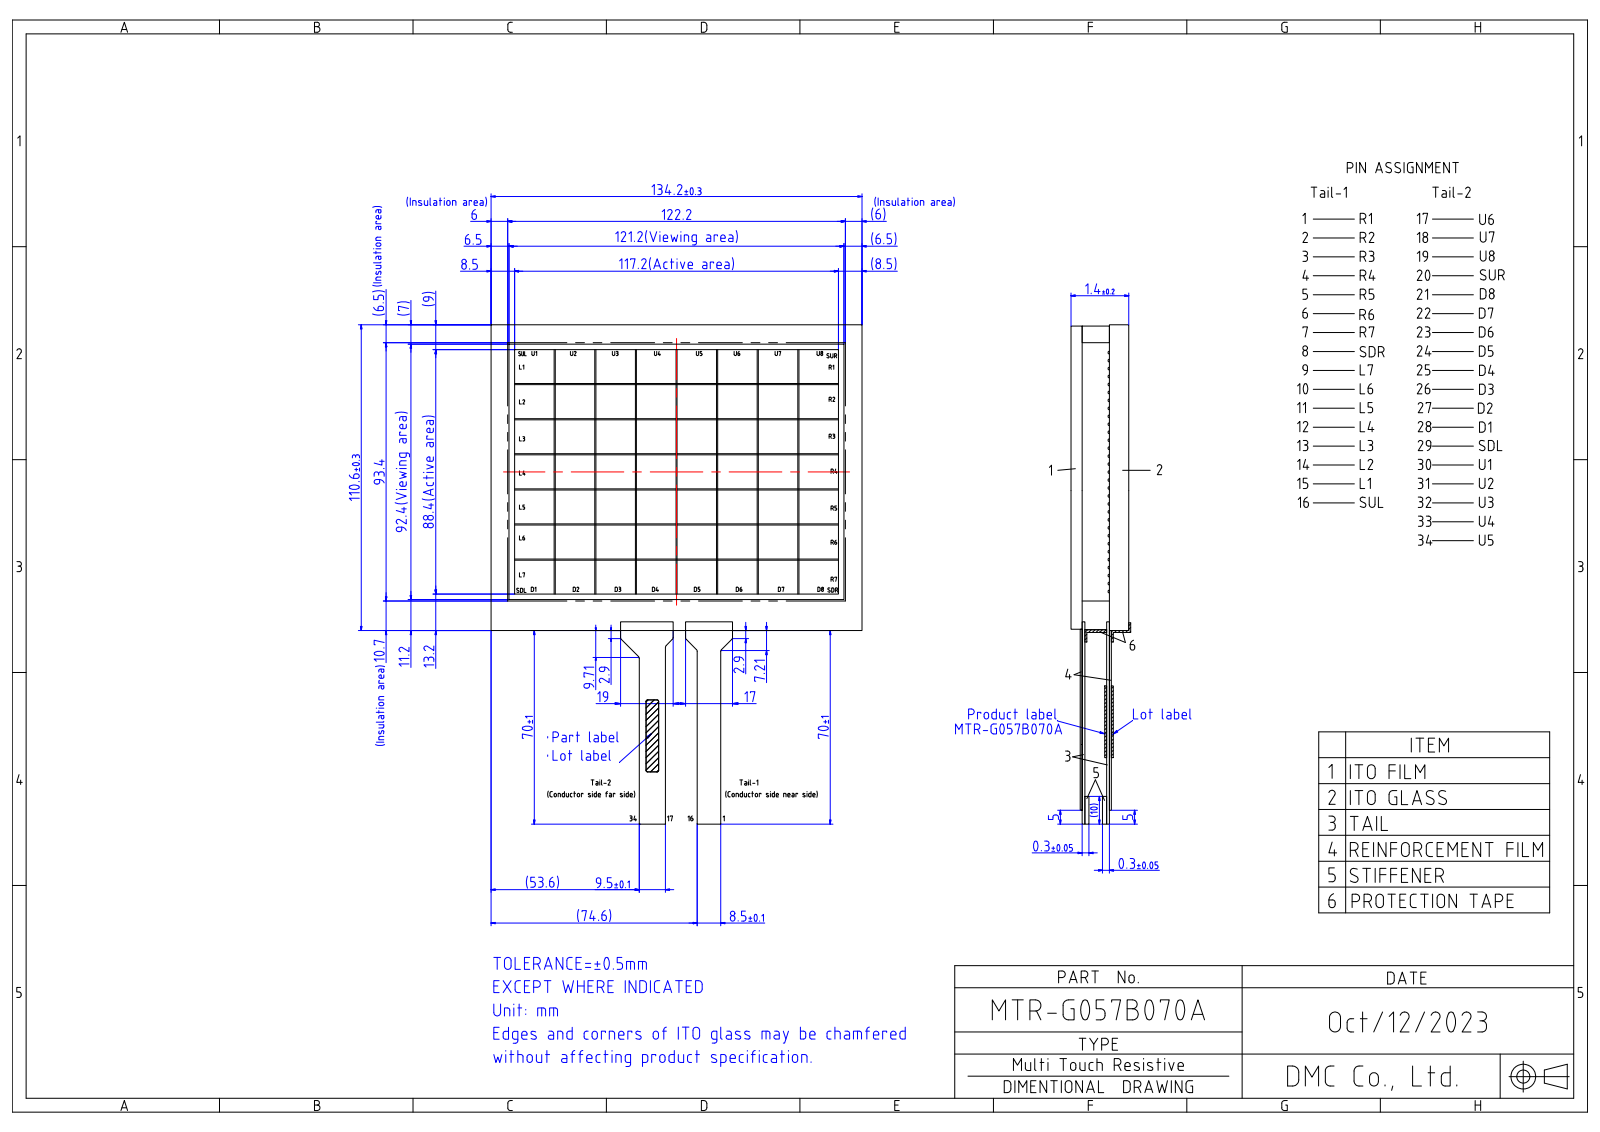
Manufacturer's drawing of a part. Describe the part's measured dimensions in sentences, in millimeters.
The part is named "MTR-G057B070A". Its 3-D file was written by "Autodesk Inventor 2020 (CONFIG_CONTROL_DESIGN)". It is 1 solid with 190 faces: 178 planar, 12 cylindrical and 0 other. Overall it measures 202.72 by 187.88 by 1.5 millimeters. Its volume is 20 875 cubic millimeters and its surface area 33 190 square millimeters. Partial cylindrical surfaces (rounded edges, fillets, slot ends): 8 of radius 1, 4 of radius 0.2. The main face-to-face distances are 1.4, 1.1, 1.2, 1.3, 110.6, 0.4, 134.2, 1.5, 0.5, 0.8.
